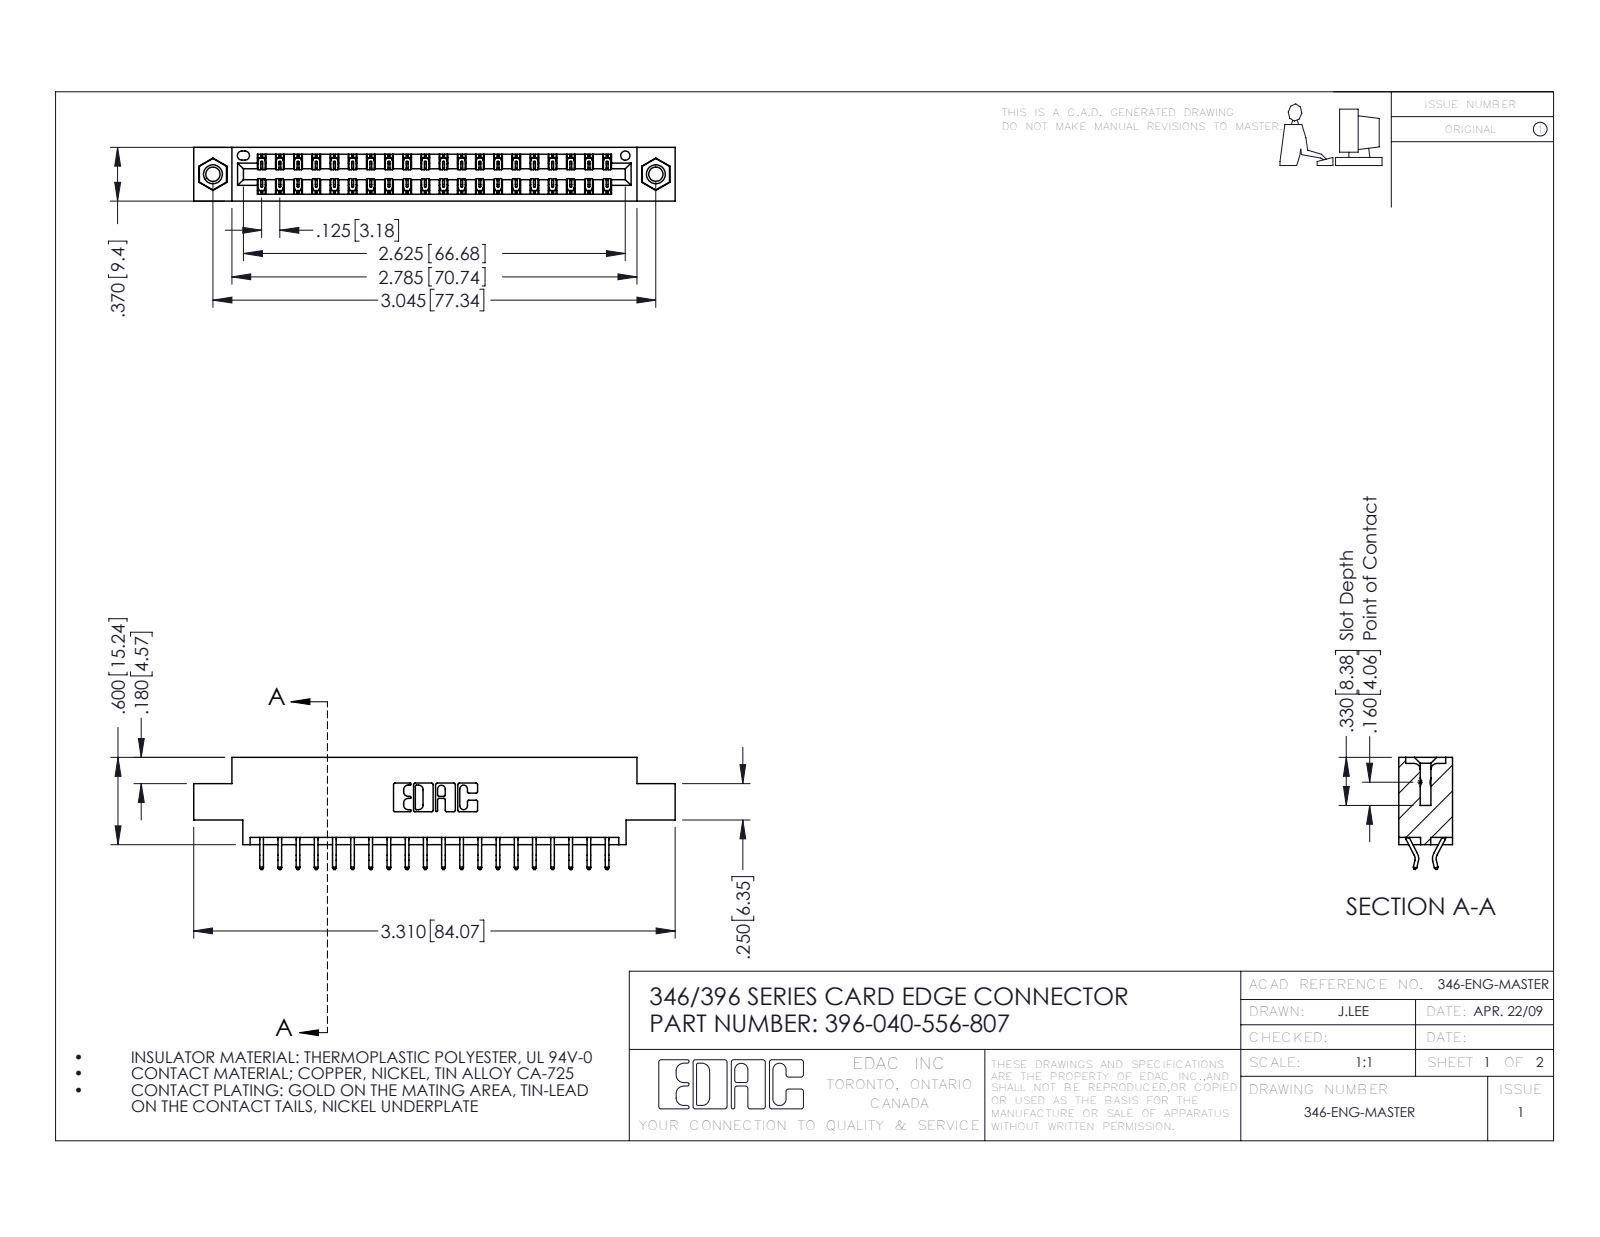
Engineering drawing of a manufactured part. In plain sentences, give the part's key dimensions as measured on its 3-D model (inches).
The part is named "346 Part_0.170 Offset - 0.156 Dia-TI; 345-250-001_345-250-005-103; 345-292-001_556 Tail; 396-040-556-807". Its 3-D file was written by "SolidWorks 2016 (CONFIG_CONTROL_DESIGN)". It is 43 solids with 2506 faces: 1672 planar, 818 cylindrical and 16 other. Overall it measures 3.31 by 0.77 by 0.37 inches. Its volume is 0.48 cubic inches and its surface area 16.48 square inches. Round holes: 2 of diameter 0.098, 2 of diameter 0.125, 2 of diameter 0.156, 1 of diameter 0.064. Round bosses or shafts: 2 of diameter 0.155. Partial cylindrical surfaces (rounded edges, fillets, slot ends): 60 of radius 0.006, 22 of radius 0.01, 6 of radius 0.007, 6 of radius 0.031, 3 of radius 0.026, 2 of radius 0.01, 2 of radius 0.014, 2 of radius 0.022. The main face-to-face distances are 0.048, 0.322, 0.37, 0.25, 0.025, 0.072, 0.298, 0.275, 0.222, 0.148. The hole center spacings are 0.246, 2.837, 3.045.
